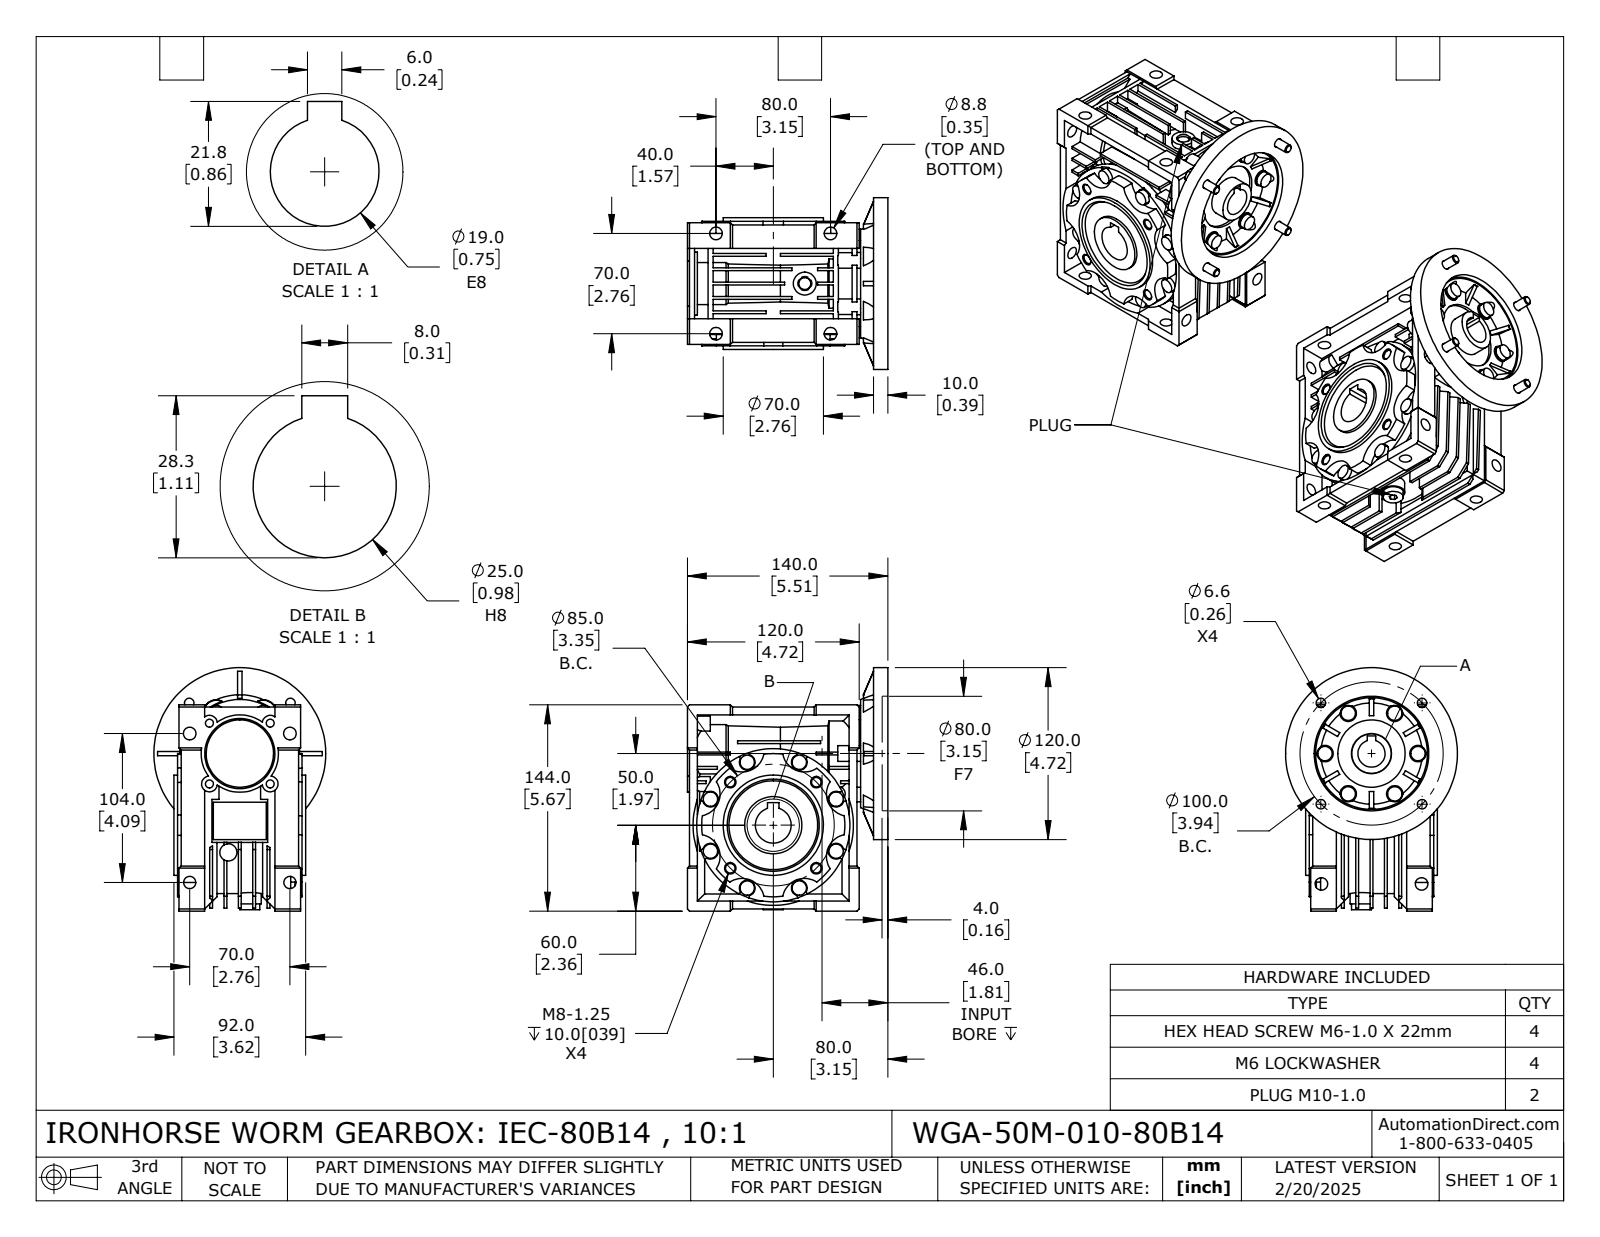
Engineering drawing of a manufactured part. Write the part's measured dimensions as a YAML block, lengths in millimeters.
part_name: "WGA-50M-010-80B14"
step_written_by: "SolidWorks 2024 (CONFIG_CONTROL_DESIGN)"
units: millimeters
bodies: {solids: 14, faces: 1080, planar: 600, cylindrical: 339, other: 141}
overall_size: [170, 150.5, 120]
volume: 1088000
surface_area: 242203
round_holes:
  - {diameter: 8.8, count: 8}
  - {diameter: 8.5, count: 6}
  - {diameter: 5.55, count: 4}
  - {diameter: 6.1, count: 4}
  - {diameter: 6.6, count: 4}
  - {diameter: 6.65, count: 2}
  - {diameter: 6.65, count: 2}
  - {diameter: 9, count: 2}
  - {diameter: 19, count: 1}
  - {diameter: 20, count: 1}
  - {diameter: 25, count: 1}
  - {diameter: 28, count: 1}
round_bosses_or_shafts:
  - {diameter: 10, count: 14}
  - {diameter: 12.2, count: 4}
  - {diameter: 6, count: 4}
  - {diameter: 16, count: 2}
  - {diameter: 120, count: 1}
  - {diameter: 107, count: 1}
  - {diameter: 70, count: 1}
  - {diameter: 61, count: 1}
partial_cylinders:
  - {radius: 5.5, count: 18}
  - {radius: 6, count: 8}
  - {radius: 15, count: 8}
  - {radius: 15.5, count: 8}
  - {radius: 5.75, count: 6}
  - {radius: 20.76, count: 1}
  - {radius: 46, count: 1}
  - {radius: 47.7, count: 1}
face_to_face_distances: [10, 2, 7, 1.5, 8, 5.5, 20, 2.5, 55, 35]
hole_center_spacings: [58.31, 80, 70, 20.01, 30, 42.42, 42.5, 50.01]
